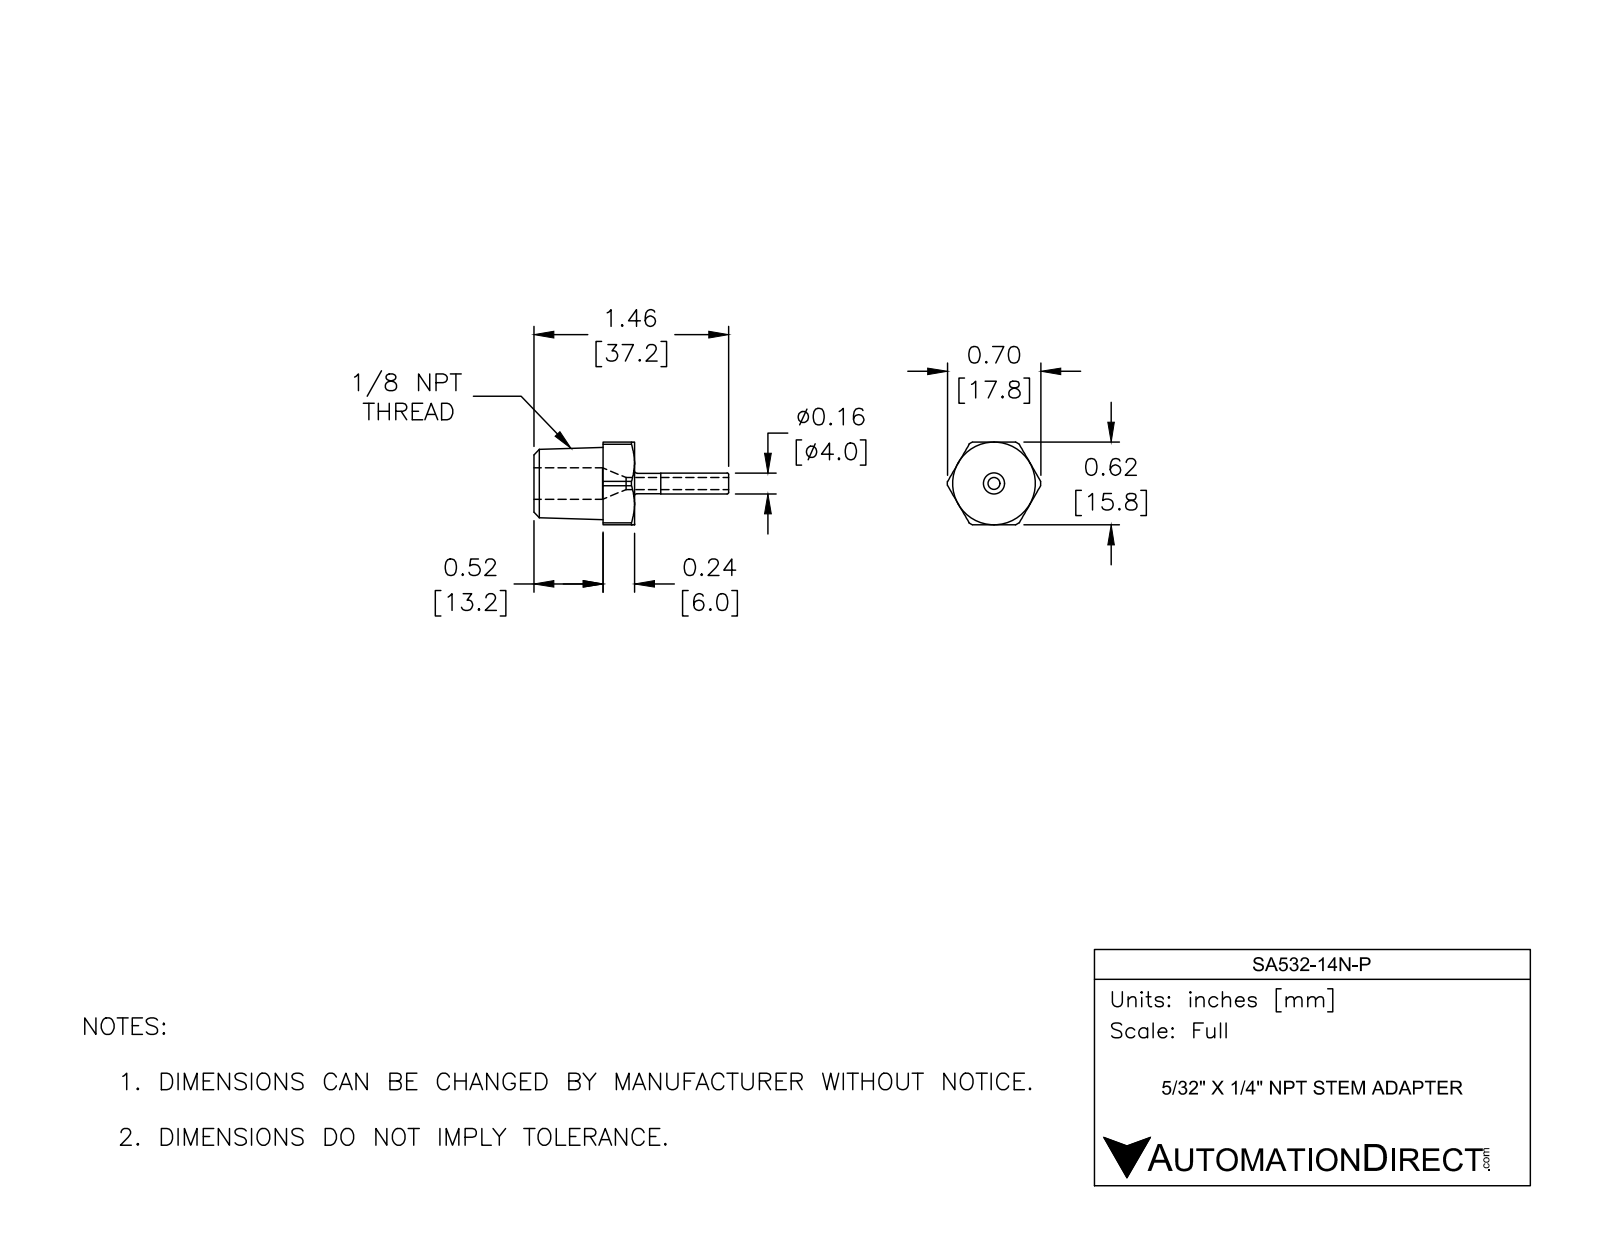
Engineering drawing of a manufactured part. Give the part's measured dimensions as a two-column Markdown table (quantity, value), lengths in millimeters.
| quantity | value |
| --- | --- |
| part name | SA532-14N-P |
| STEP written by | SolidWorks 2017 (AUTOMOTIVE_DESIGN) |
| units | millimeters |
| bodies | 1 solid, 41 faces (11 planar, 14 cylindrical, 16 other) |
| overall size | 37.2 × 17.8 × 15.8 |
| volume | 2 830 mm³ |
| surface area | 1 901 mm² |
| round holes (diameter × count) | 2.3 × 1, 6 × 1 |
| round bosses / shafts (diameter × count) | 4 × 1, 3.9 × 1 |
| partial cylindrical surfaces (radius × count) | 8.9 × 1 |
| main face-to-face distances | 15.8, 19.2, 13.2, 6, 37.2, 24, 18, 24.2, 11, 5 |
